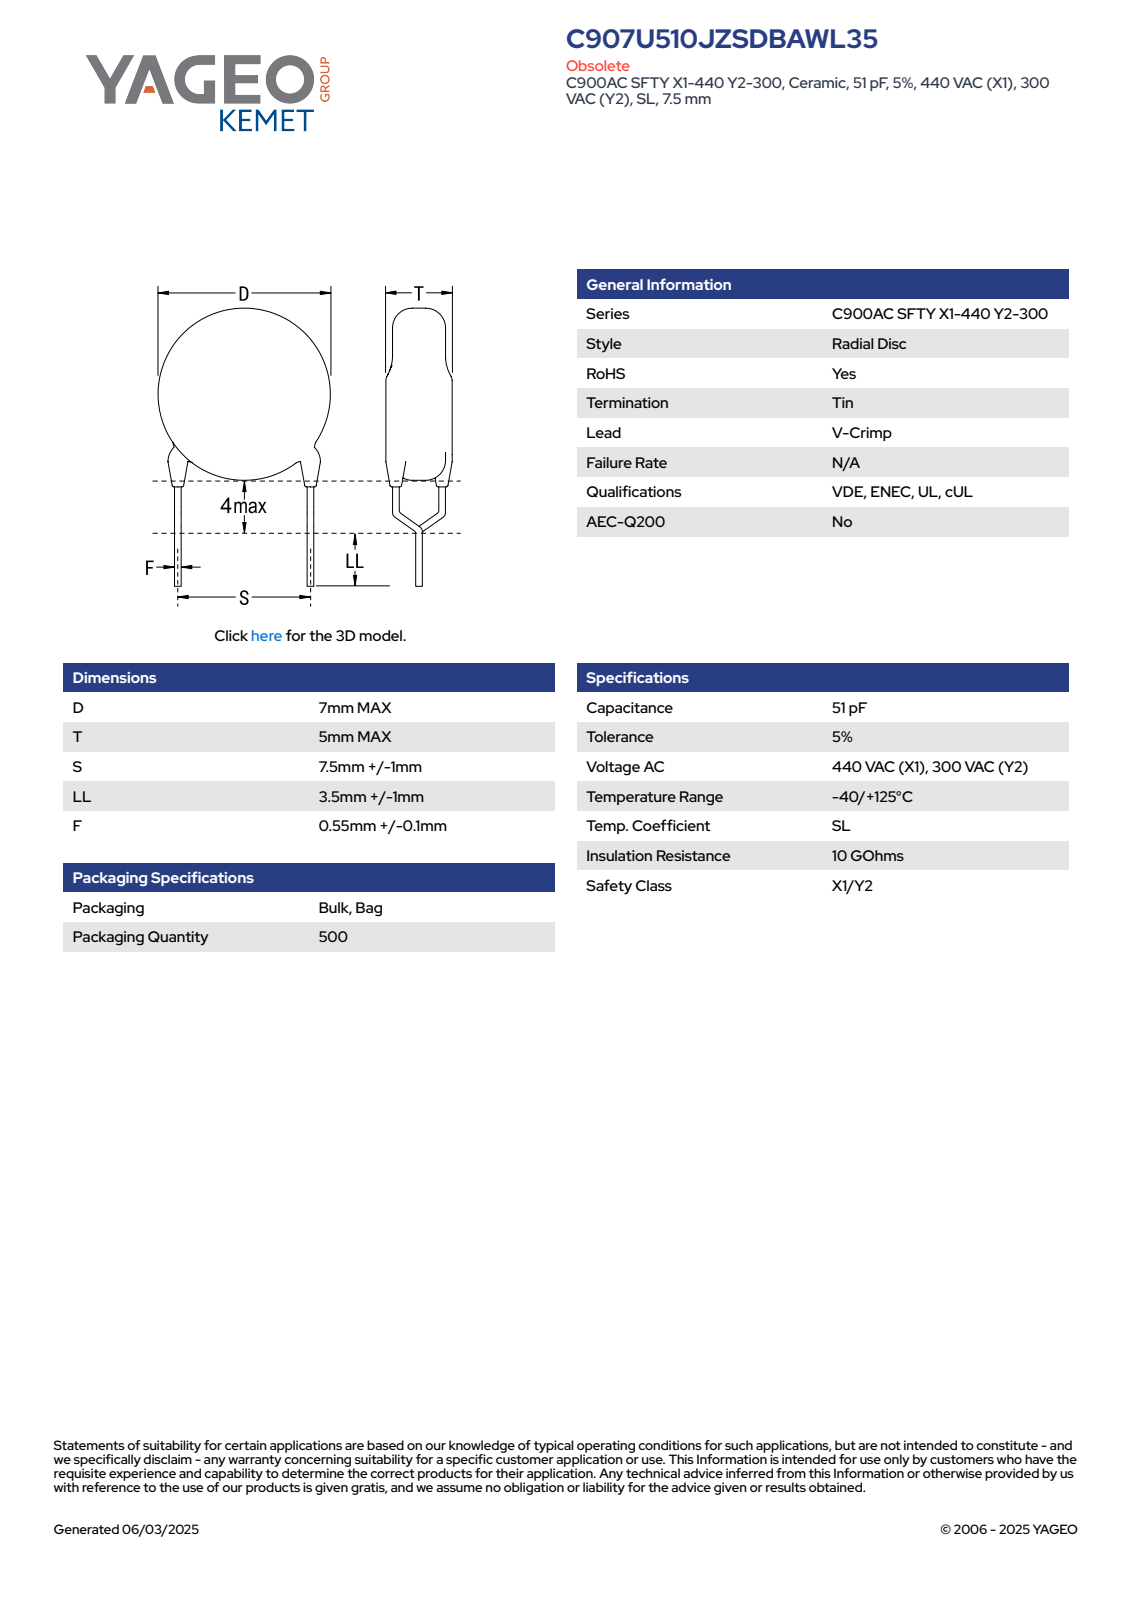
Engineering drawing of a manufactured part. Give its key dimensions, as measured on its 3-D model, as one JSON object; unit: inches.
{"part_name": "CCD_VCC900_D7T5S7.5LL4.5F0.65", "step_written_by": "SolidWorks 2014 (AUTOMOTIVE_DESIGN)", "units": "inches", "bodies": {"solids": 5, "faces": 93, "planar": 65, "cylindrical": 16, "other": 12}, "overall_size": [0.602, 0.321, 0.197], "volume_in3": 0.012, "surface_area_in2": 0.338, "round_bosses_or_shafts": [[0.026, 6], [0.276, 1]], "face_to_face_distances": [0.197, 0.291, 0.036, 0.482, 0.191, 0.446, 0.155, 0.146, 0.013, 0.074]}
